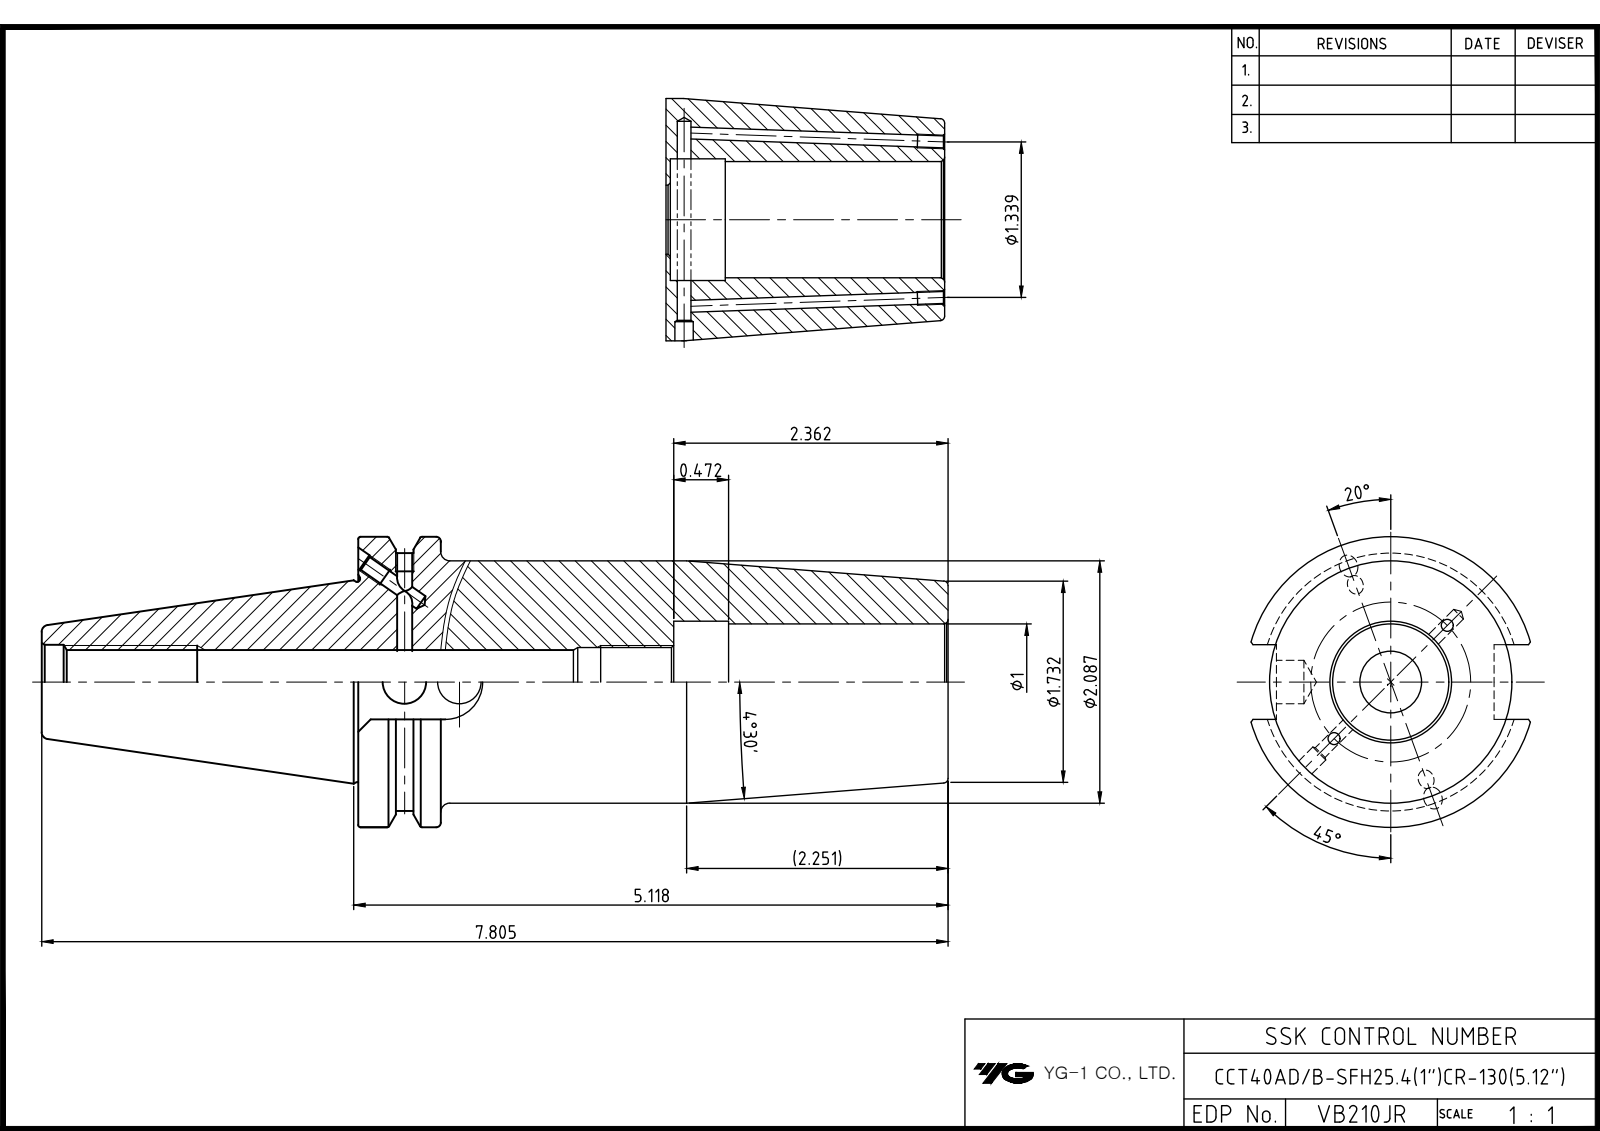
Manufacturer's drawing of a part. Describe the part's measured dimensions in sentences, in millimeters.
The part is named "LO-CCT40ADB-SFH25.4CR-130". Its 3-D file was written by "Autodesk Inventor 2026 (AUTOMOTIVE_DESIGN)". It is 1 solid with 88 faces: 34 planar, 31 cylindrical and 23 other. Overall it measures 198.25 by 63.5 by 61.09 millimeters. Its volume is 288 088 cubic millimeters and its surface area 45 959 square millimeters. Round holes: 4 of diameter 3.24, 2 of diameter 2.46, 2 of diameter 4, 2 of diameter 4.2, 1 of diameter 9.53, 1 of diameter 13.39, 1 of diameter 14.92, 1 of diameter 16.3, 1 of diameter 25.4, 1 of diameter 26.6. Round bosses or shafts: 1 of diameter 63.5, 1 of diameter 53. Partial cylindrical surfaces (rounded edges, fillets, slot ends): 1 of radius 8.19, 1 of radius 28.15. The main face-to-face distances are 129, 69, 60, 47.6, 18.05, 50.95, 110.95, 16.38, 69.25, 87.3.
